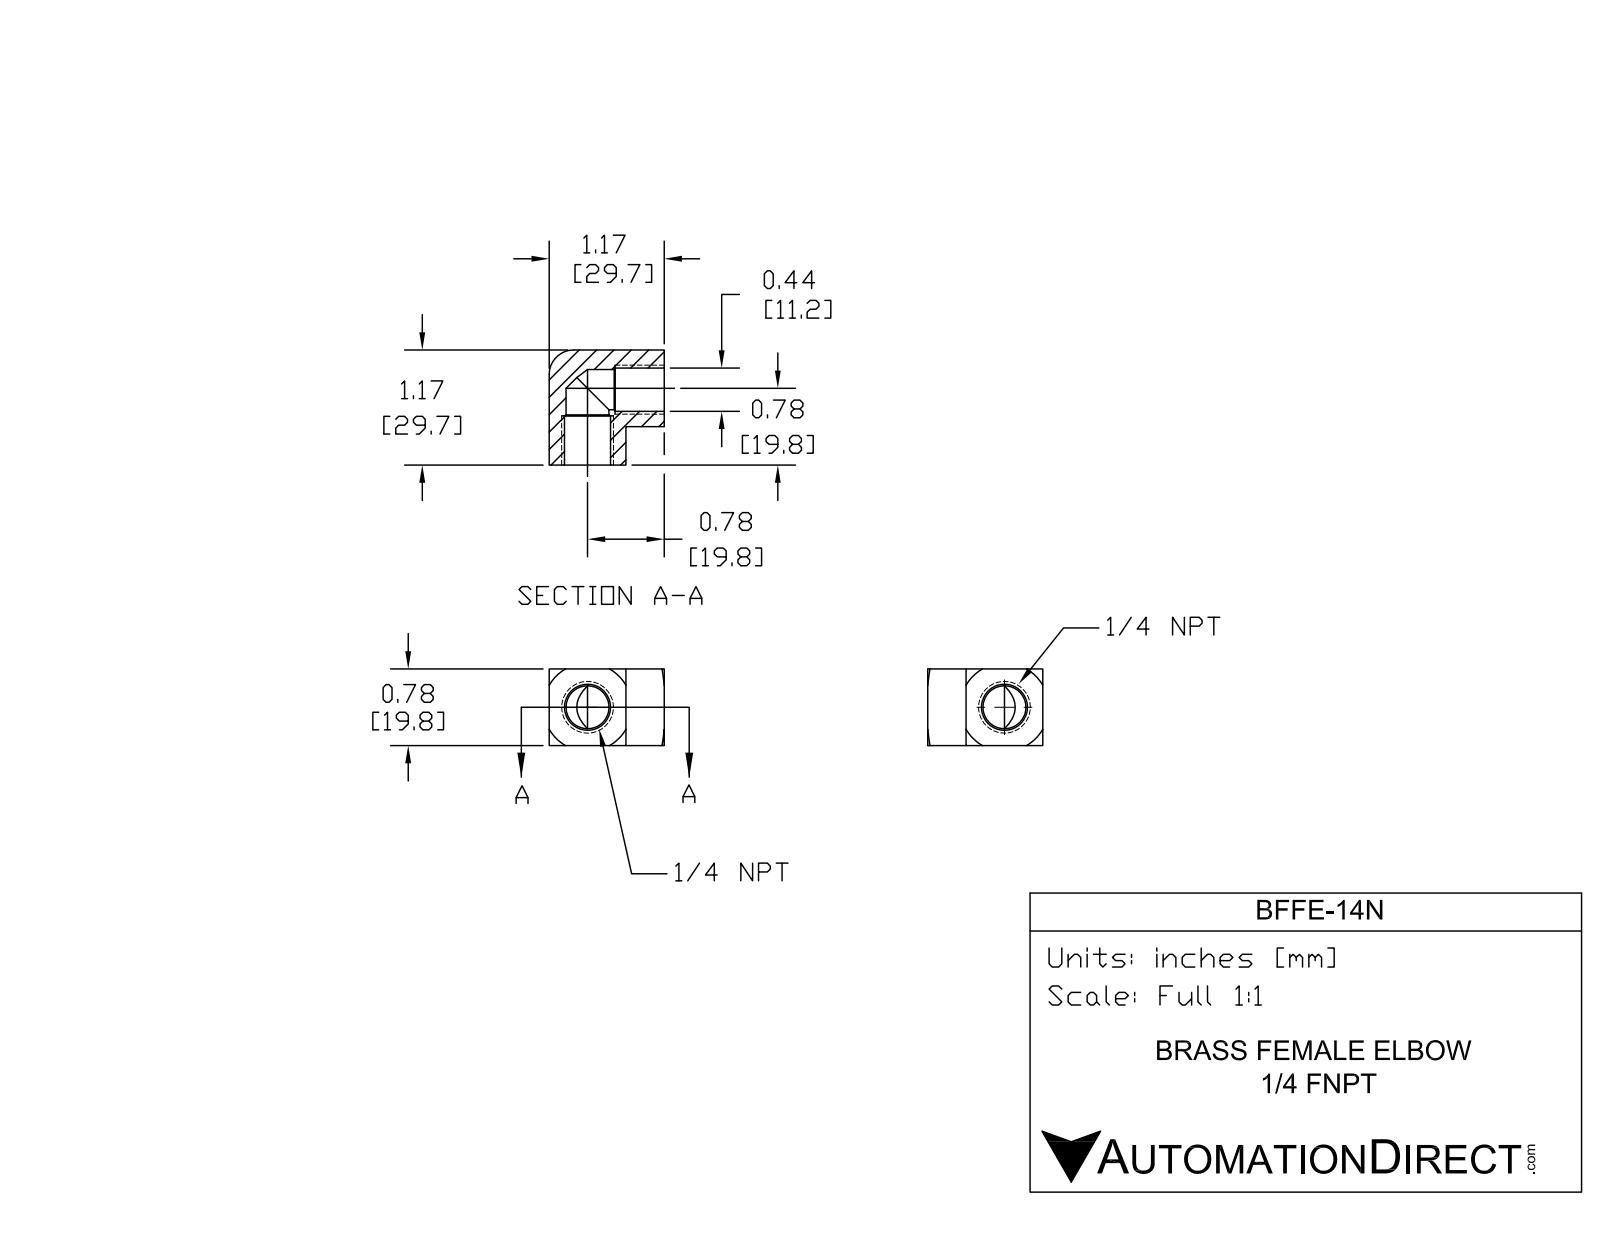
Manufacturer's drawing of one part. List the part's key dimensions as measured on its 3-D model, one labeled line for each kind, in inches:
Part name (STEP PRODUCT): BFFE-14N
STEP written by: SolidWorks 2015 (CONFIG_CONTROL_DESIGN)
Units: inches
Bodies: 1 solid, 32 faces (8 planar, 9 cylindrical, 15 other)
Overall size (bounding box): 1.17 × 1.17 × 0.78
Volume: 0.69 in³ · Surface area: 7.8 in²
Round holes (diameter × count): ⌀0.437 ×2, ⌀0.468 ×2
Partial cylindrical surfaces — rounded edges, fillets, slot ends (radius × count): R0.25 ×1
Main face-to-face distances: 0.78, 1.17, 0.39
